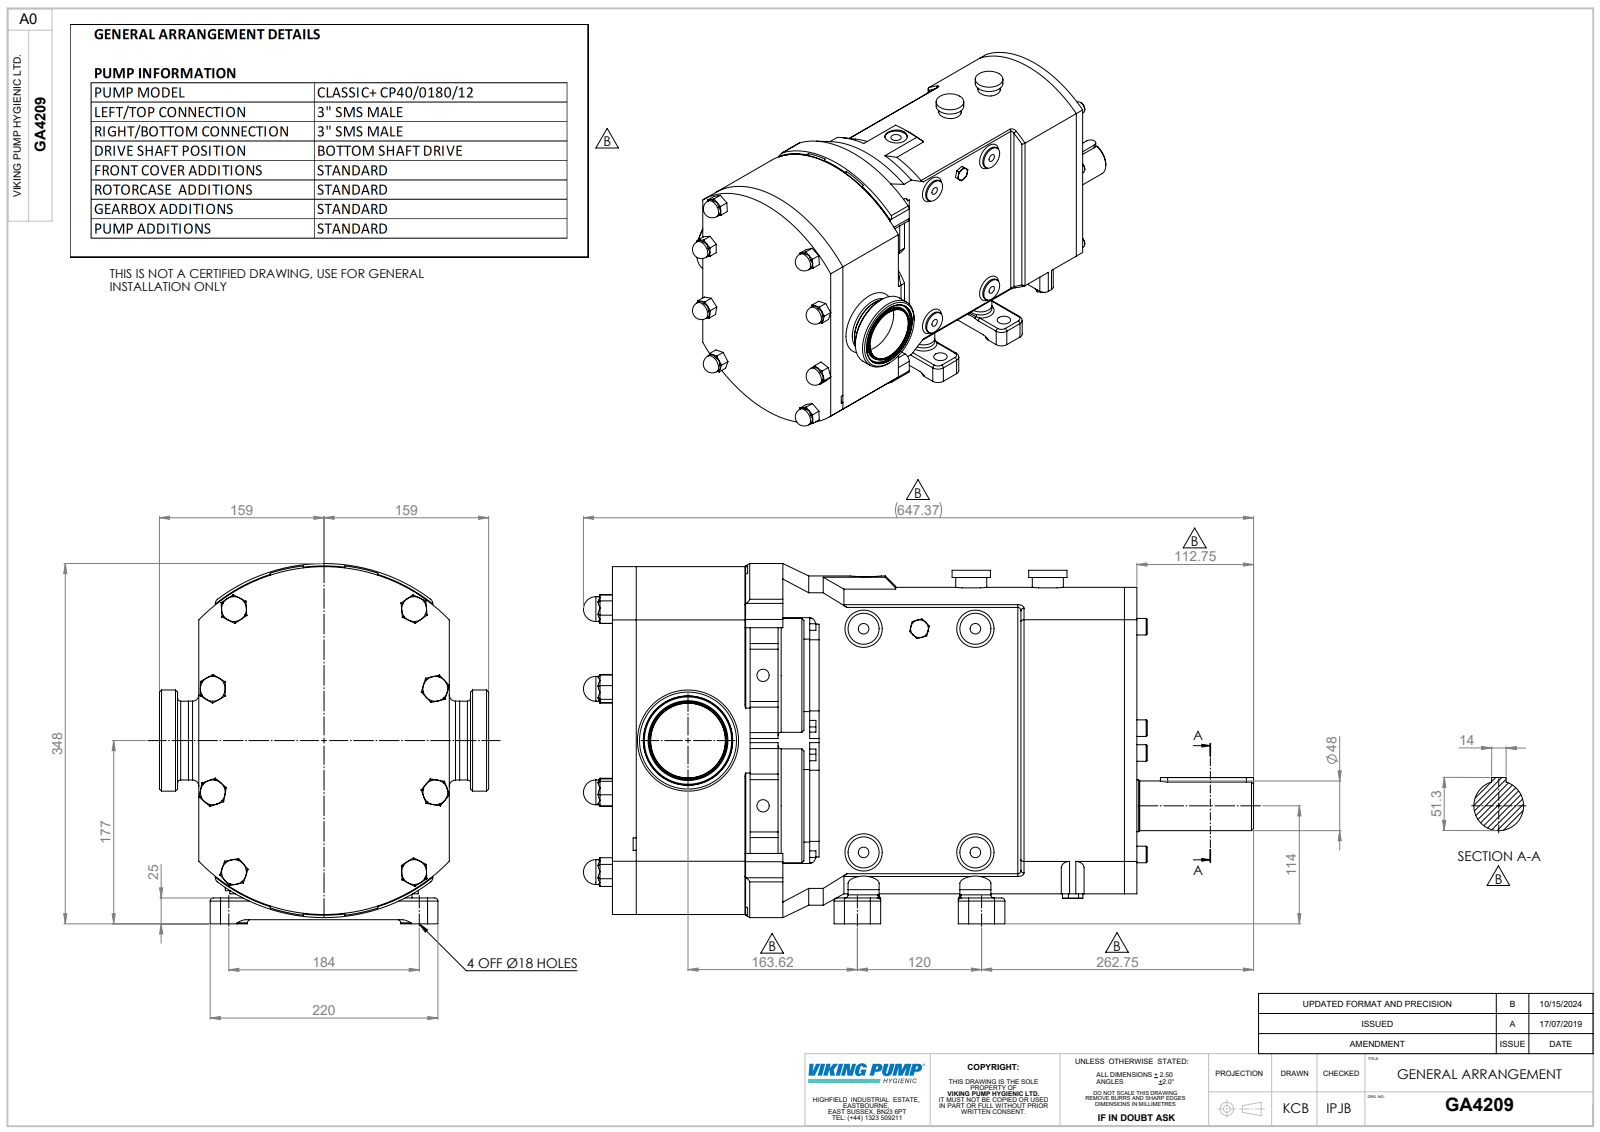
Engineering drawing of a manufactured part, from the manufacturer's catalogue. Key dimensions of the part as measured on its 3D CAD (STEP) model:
Part name (STEP PRODUCT): Copy of CP40S-0180 H BSD^GA4209; GA4209; Copy of Z94-5101-55 - 3 INCH SMS681^GA4209
STEP written by: SolidWorks 2023 (AUTOMOTIVE_DESIGN)
Units: millimetres
Bodies: 3 solids, 977 faces (369 planar, 279 cylindrical, 329 other)
Overall size (bounding box): 647.37 × 348 × 318
Volume: 26 350 000 mm³ · Surface area: 909 432 mm²
Round holes (diameter × count): ⌀10.2 ×4, ⌀18 ×4, ⌀11.89 ×2, ⌀35 ×2, ⌀13.83 ×1, ⌀30 ×1, ⌀72.2 ×1, ⌀86 ×1
Round bosses / shafts (diameter × count): ⌀30 ×10, ⌀24 ×8, ⌀16 ×6, ⌀110 ×2, ⌀70 ×2, ⌀37 ×2, ⌀31.75 ×2, ⌀250 ×1
Partial cylindrical surfaces — rounded edges, fillets, slot ends (radius × count): R10 ×24, R3 ×22, R8 ×20, R6 ×10, R5 ×4, R11 ×4, R7 ×2, R13 ×2
Main face-to-face distances: 21, 30, 161, 51, 191, 212, 140, 506.62, 182, 242
Hole centre spacings: 92.35, 92.54, 96.05, 107.04, 108, 112.07, 120, 143.4
